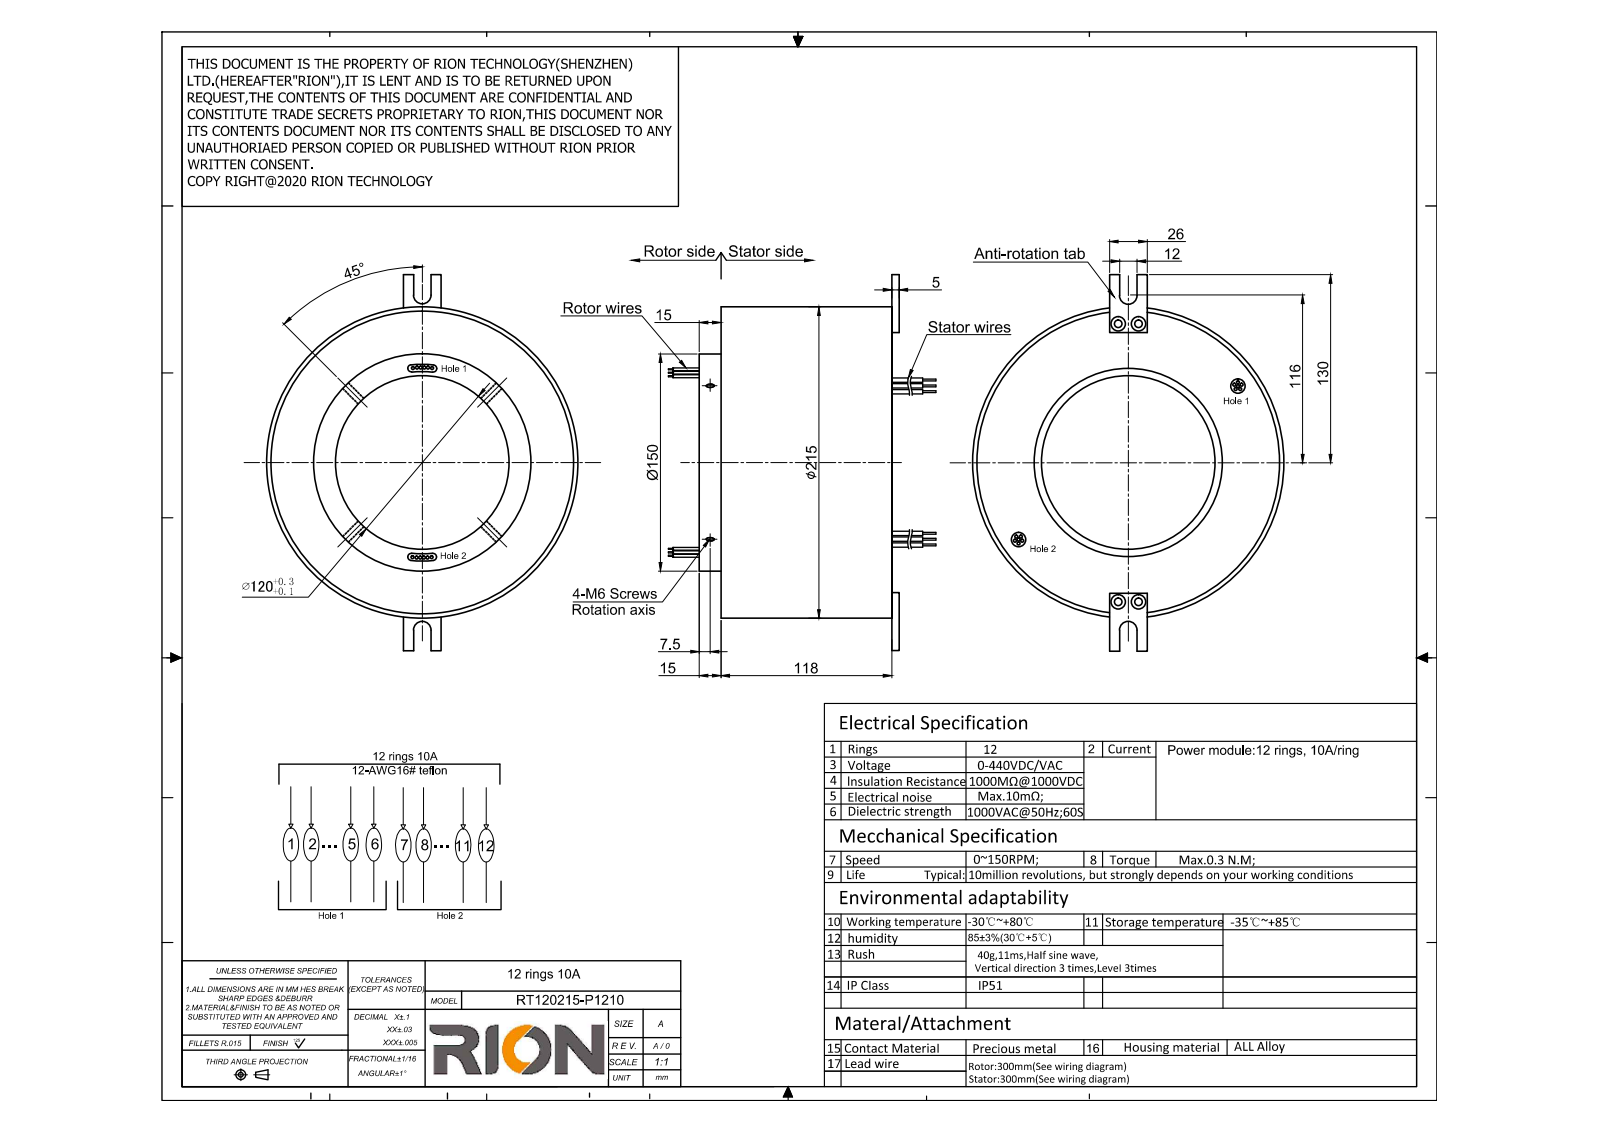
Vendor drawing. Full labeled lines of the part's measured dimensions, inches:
Part name (STEP PRODUCT): RT120215-P1210
STEP written by: SolidWorks 2014 (CONFIG_CONTROL_DESIGN)
Units: inches
Bodies: 1 solid, 184 faces (62 planar, 106 cylindrical, 16 other)
Overall size (bounding box): 10.236 × 8.661 × 8.465
Volume: 186.3 in³ · Surface area: 331.3 in²
Round holes (diameter × count): ⌀0.197 ×8, ⌀0.165 ×4, ⌀0.394 ×2, ⌀4.724 ×1, ⌀5.126 ×1, ⌀8.236 ×1
Round bosses / shafts (diameter × count): ⌀0.083 ×24, ⌀8.465 ×1, ⌀8.228 ×1, ⌀5.906 ×1, ⌀5.118 ×1
Partial cylindrical surfaces — rounded edges, fillets, slot ends (radius × count): R0.098 ×4, R0.236 ×2, R2.48 ×1, R2.677 ×1
Main face-to-face distances: 4.646, 0.591, 5.236, 0.197, 5.433, 4.843, 0.276, 1.024, 0.748, 8.661
Hole centre spacings: 3.789, 0.551, 3.192, 3.642, 3.671, 6.463, 6.713, 7.559
